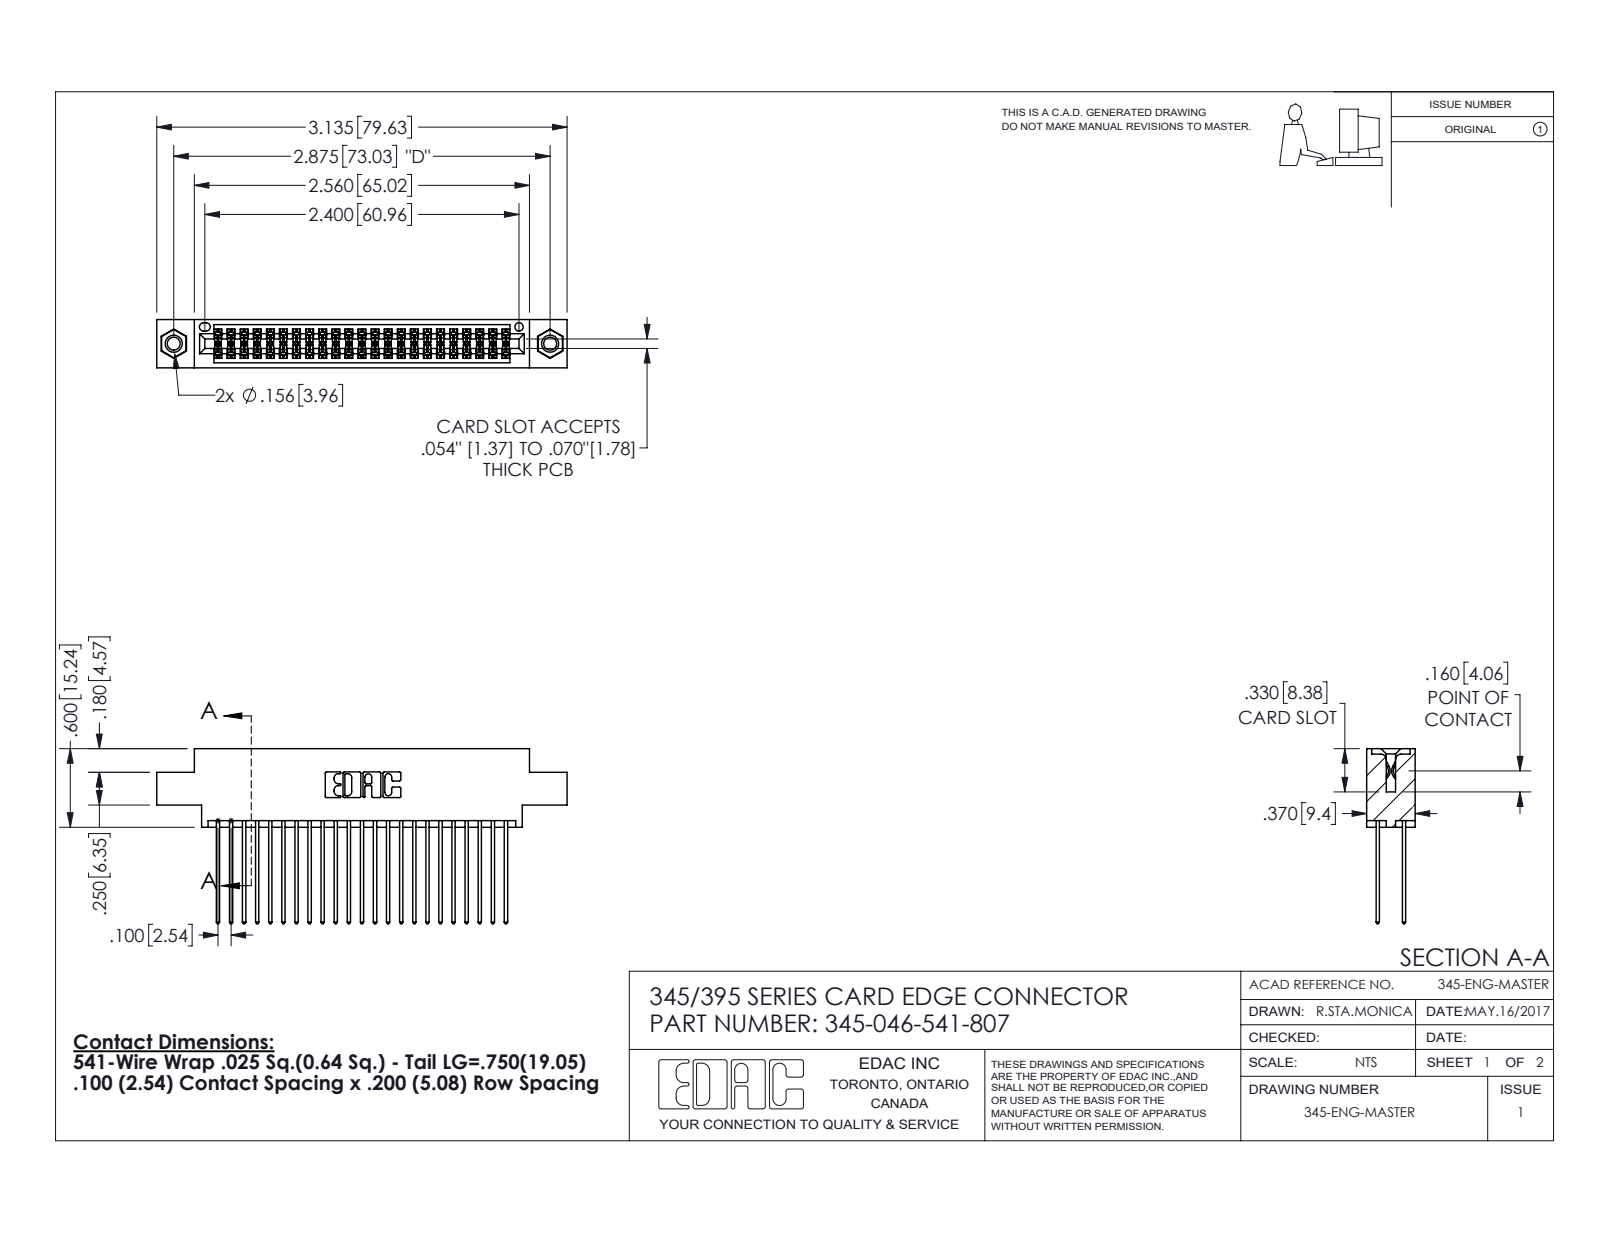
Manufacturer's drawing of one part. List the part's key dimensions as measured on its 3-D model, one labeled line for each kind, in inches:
Part name (STEP PRODUCT): 345-046-541-807; 345-250-001_345-250-005-103; 345 Part_0.170 Offset - 0.156 Dia-TI; 345-292-001_345-293-141
STEP written by: SolidWorks 2016 (CONFIG_CONTROL_DESIGN)
Units: inches
Bodies: 49 solids, 2490 faces (1634 planar, 840 cylindrical, 16 other)
Overall size (bounding box): 3.135 × 1.337 × 0.37
Volume: 0.47 in³ · Surface area: 19.25 in²
Round holes (diameter × count): ⌀0.098 ×2, ⌀0.125 ×2, ⌀0.156 ×2, ⌀0.064 ×1
Round bosses / shafts (diameter × count): ⌀0.155 ×2
Partial cylindrical surfaces — rounded edges, fillets, slot ends (radius × count): R0.006 ×69, R0.01 ×46, R0.01 ×22, R0.007 ×6, R0.031 ×6, R0.026 ×3, R0.014 ×2, R0.019 ×2
Main face-to-face distances: 0.072, 0.298, 0.2, 0.098, 0.272, 0.025, 0.37, 0.225, 0.175, 0.149
Hole centre spacings: 0.27, 2.641, 2.875
